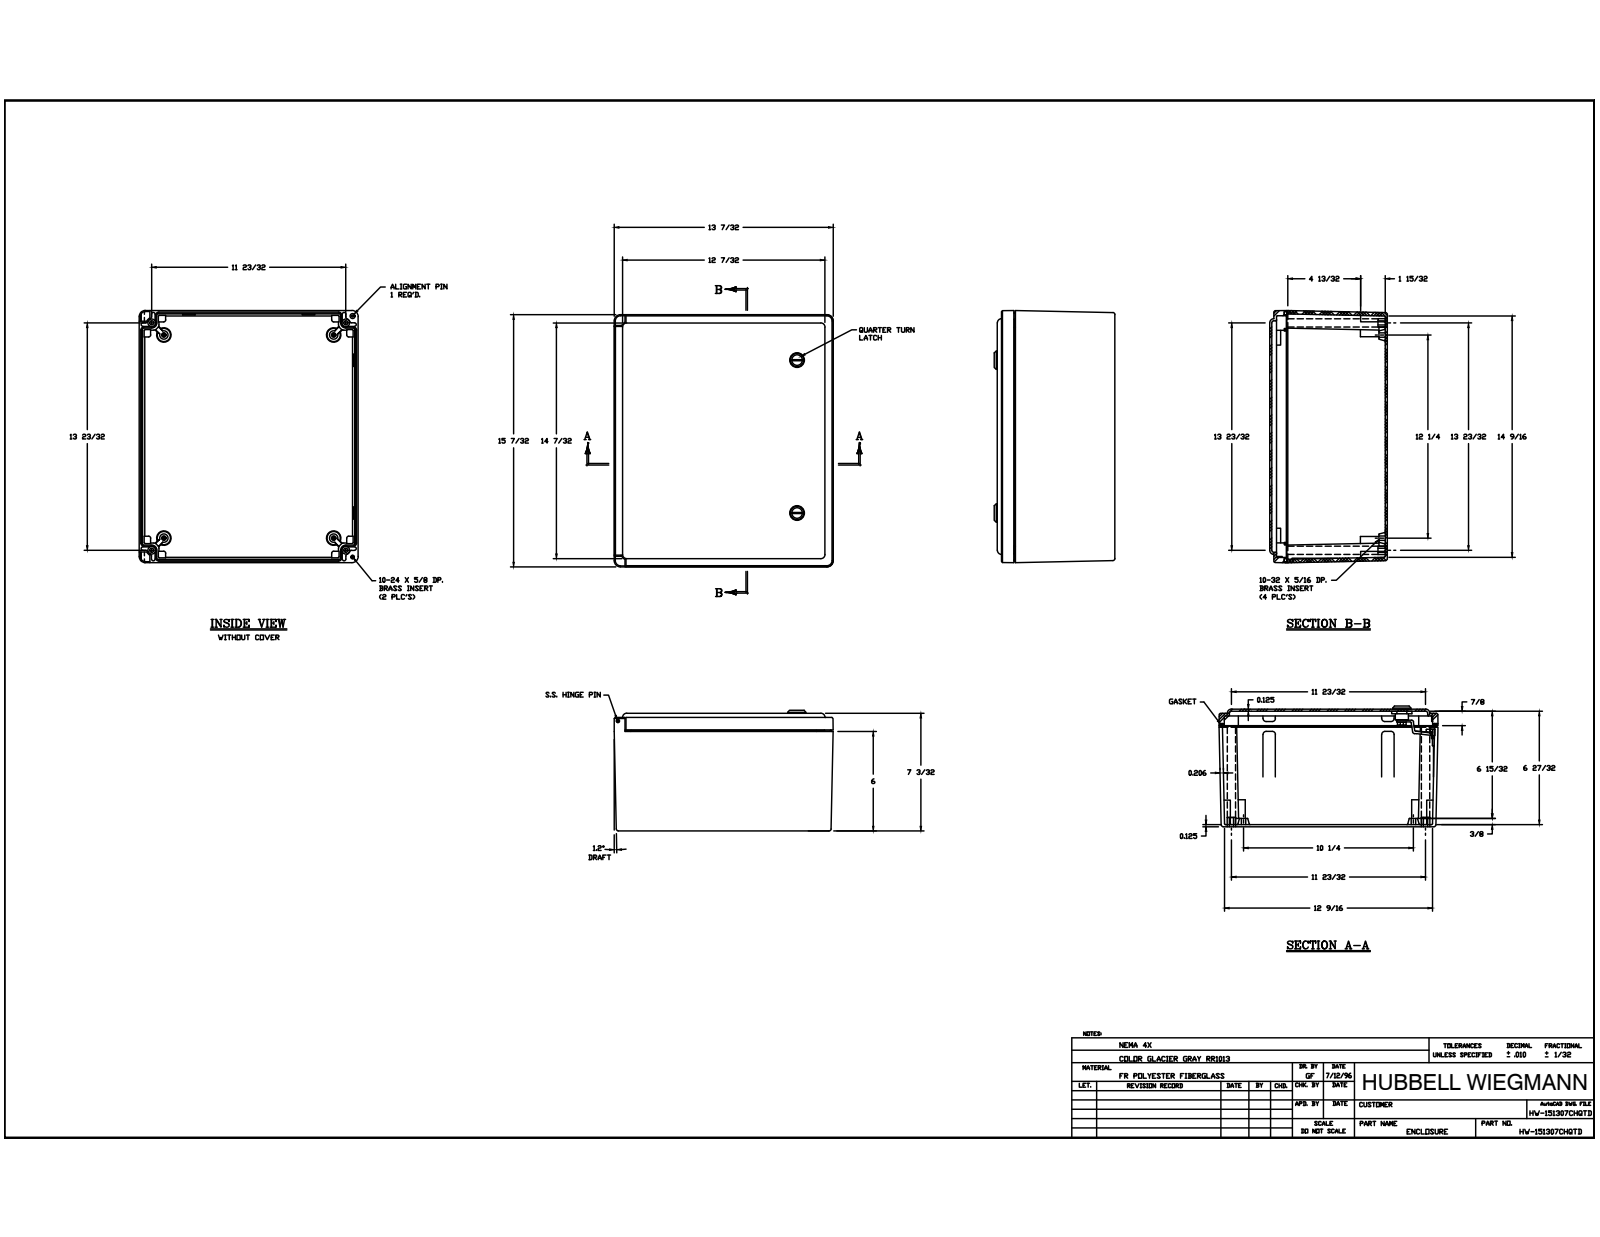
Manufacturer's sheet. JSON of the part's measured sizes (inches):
{"part_name": "WP1513HLBOX; 0.3125-18 X 0.563 DP BRASS INSERT; 10-32 X0.3125 DP BRASS INSERT; 10-24 X 0.625 DP BRASS INSERT (+8 more)", "step_written_by": "Autodesk Inventor 2014 (AUTOMOTIVE_DESIGN)", "units": "inches", "bodies": {"solids": 39, "faces": 1294, "planar": 569, "cylindrical": 385, "other": 340}, "overall_size": [15.22, 13.225, 7.281], "volume_in3": 140.5, "surface_area_in2": 1714, "round_holes": [[0.281, 6], [0.104, 4], [0.13, 4], [0.14, 4], [0.156, 4], [0.313, 4], [0.531, 4], [0.096, 2], [0.145, 2], [0.15, 2], [0.156, 2], [0.179, 2]], "round_bosses_or_shafts": [[1.094, 2], [0.63, 2], [0.4, 2], [0.375, 2], [0.371, 2], [0.367, 2], [0.25, 2], [0.234, 2]], "partial_cylinders_radius": [[0.031, 60], [0.125, 40], [0.063, 29], [0.313, 16], [0.156, 10], [0.059, 8], [0.187, 8], [0.188, 8]], "face_to_face_distances": [0.125, 6.969, 0.186, 7.094, 6.844, 0.125, 0.25, 6.844, 6.719, 0.75], "hole_center_spacings": [1.039, 11.01, 13.007, 17.009, 8.688, 0.014, 0.528, 0.572]}
